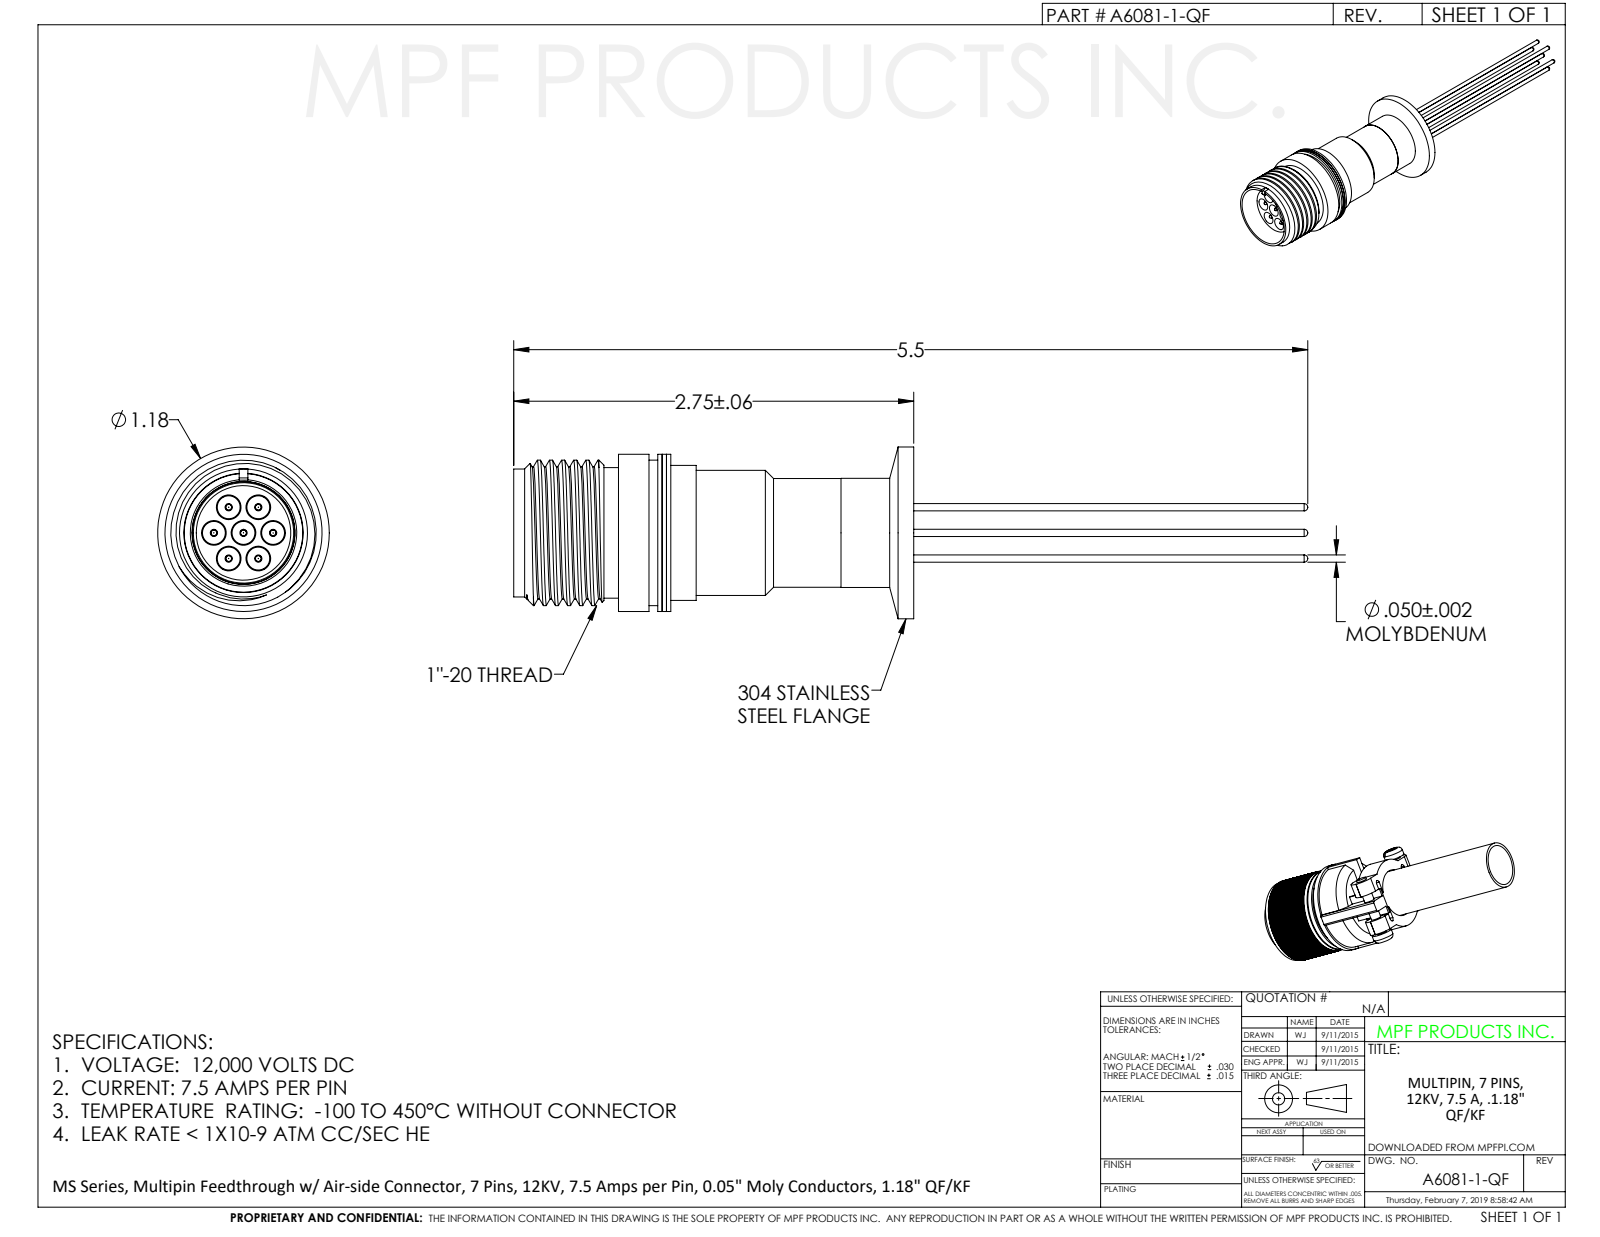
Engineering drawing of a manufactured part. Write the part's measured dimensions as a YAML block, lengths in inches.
part_name: "A6081-1-CF"
step_written_by: "SolidWorks 2011 (CONFIG_CONTROL_DESIGN)"
units: inches
bodies: {solids: 1, faces: 387, planar: 58, cylindrical: 159, other: 170}
overall_size: [5.455, 1.18, 1.18]
volume: 1.052
surface_area: 33.83
round_holes:
  - {diameter: 0.054, count: 7}
  - {diameter: 0.152, count: 7}
  - {diameter: 0.625, count: 1}
  - {diameter: 0.683, count: 1}
  - {diameter: 0.687, count: 1}
  - {diameter: 0.791, count: 1}
  - {diameter: 0.8, count: 1}
  - {diameter: 0.82, count: 1}
round_bosses_or_shafts:
  - {diameter: 0.117, count: 7}
  - {diameter: 0.05, count: 7}
  - {diameter: 0.04, count: 7}
  - {diameter: 1.18, count: 1}
  - {diameter: 1.08, count: 1}
  - {diameter: 1, count: 1}
  - {diameter: 0.954, count: 1}
  - {diameter: 0.928, count: 1}
face_to_face_distances: [0.241, 1.167, 0.926, 0.281, 0.04, 0.886, 1.207, 0.966, 0.926, 0.04]
hole_center_spacings: [0.204, 0.352, 0.407, 0.203, 0.353]
